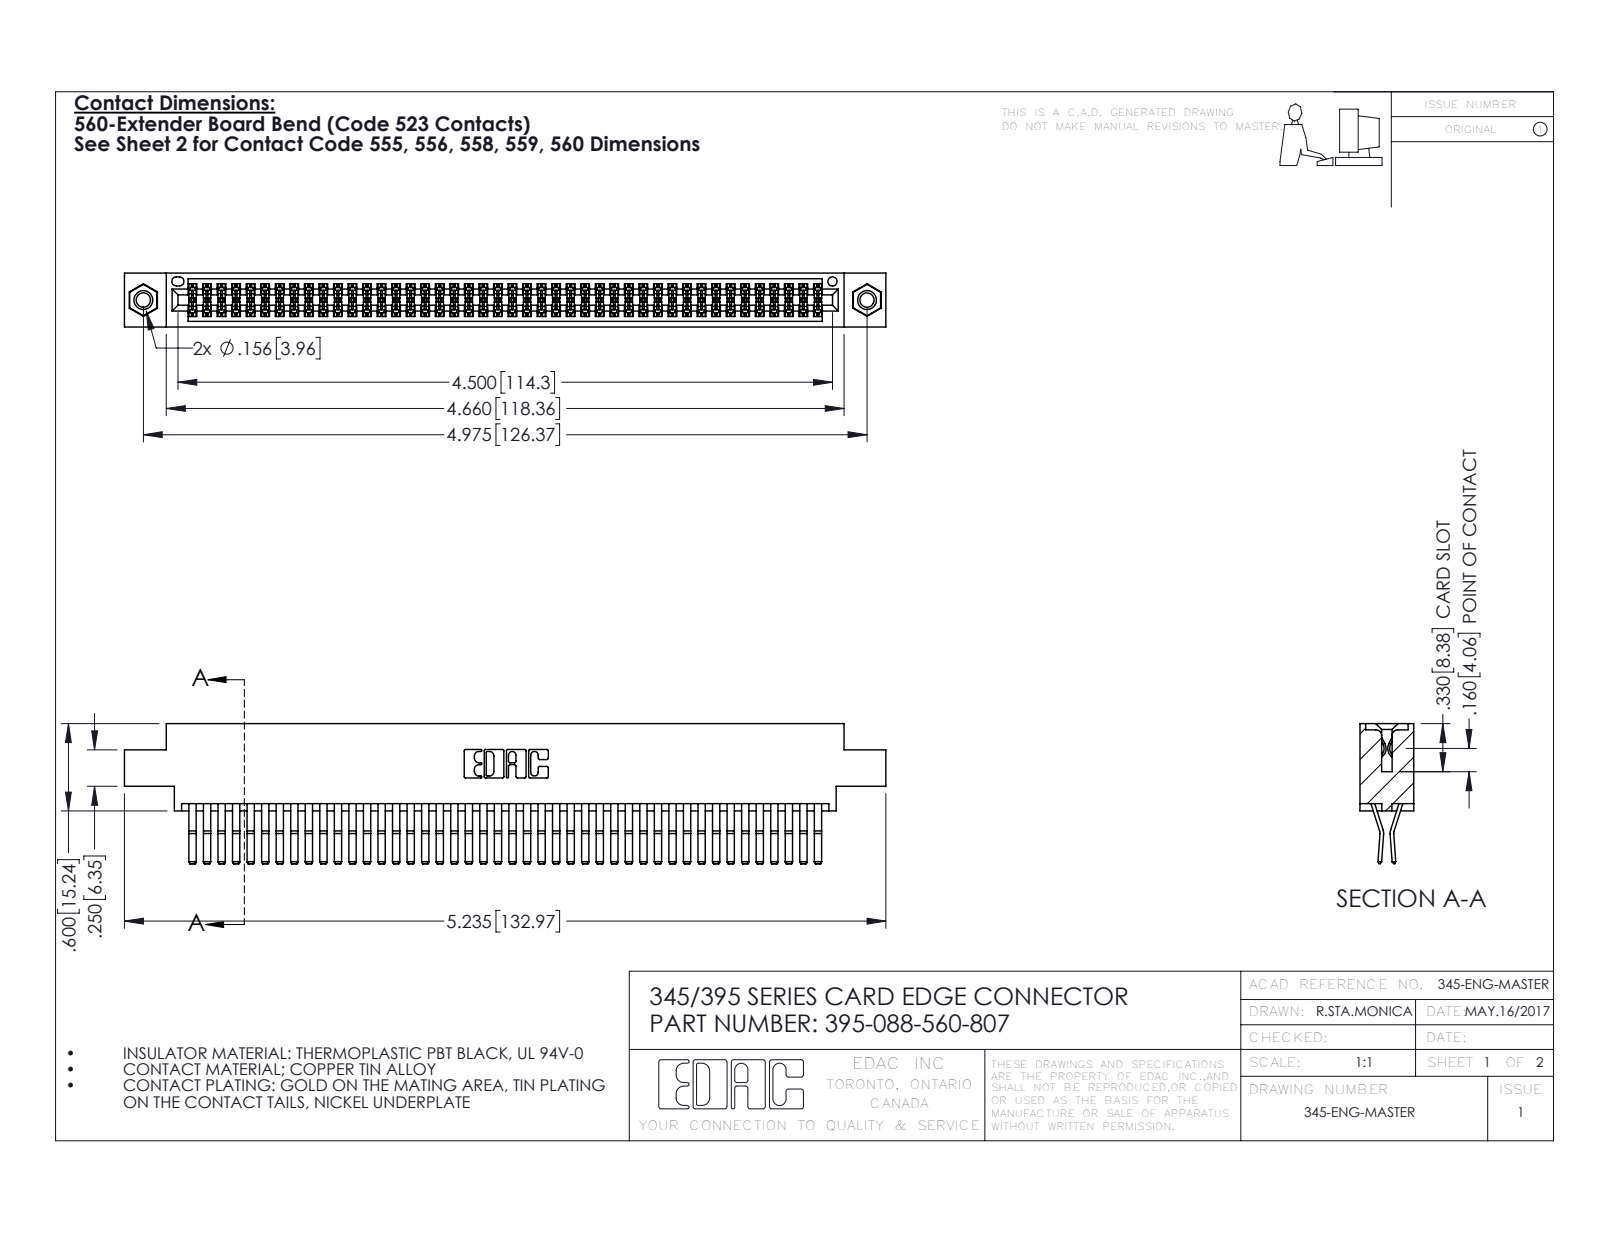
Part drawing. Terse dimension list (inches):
name: 345-292-001_560 Tail; 345 Part_0.170 Offset - 0.156 Dia-TI; 395-088-560-807; 345-250-001_345-250-005-103
written by: SolidWorks 2016 (CONFIG_CONTROL_DESIGN)
unit: in
bodies: 91 solids, 4766 faces (3020 planar, 1730 cylindrical, 16 other)
size: 5.235 × 0.962 × 0.37
volume: 0.817 in³; area: 33.29 in²
holes: 2× ⌀0.098, 2× ⌀0.125, 2× ⌀0.156, 1× ⌀0.064
bosses: 2× ⌀0.155
rounds: 132× R0.006, 22× R0.01, 6× R0.007, 6× R0.031, 3× R0.026, 2× R0.01, 2× R0.014, 2× R0.019
face distances: 0.025, 0.072, 0.298, 0.37, 0.2, 0.098, 0.272, 0.225, 0.175, 0.149
hole spacings: 0.27, 4.739, 4.975
